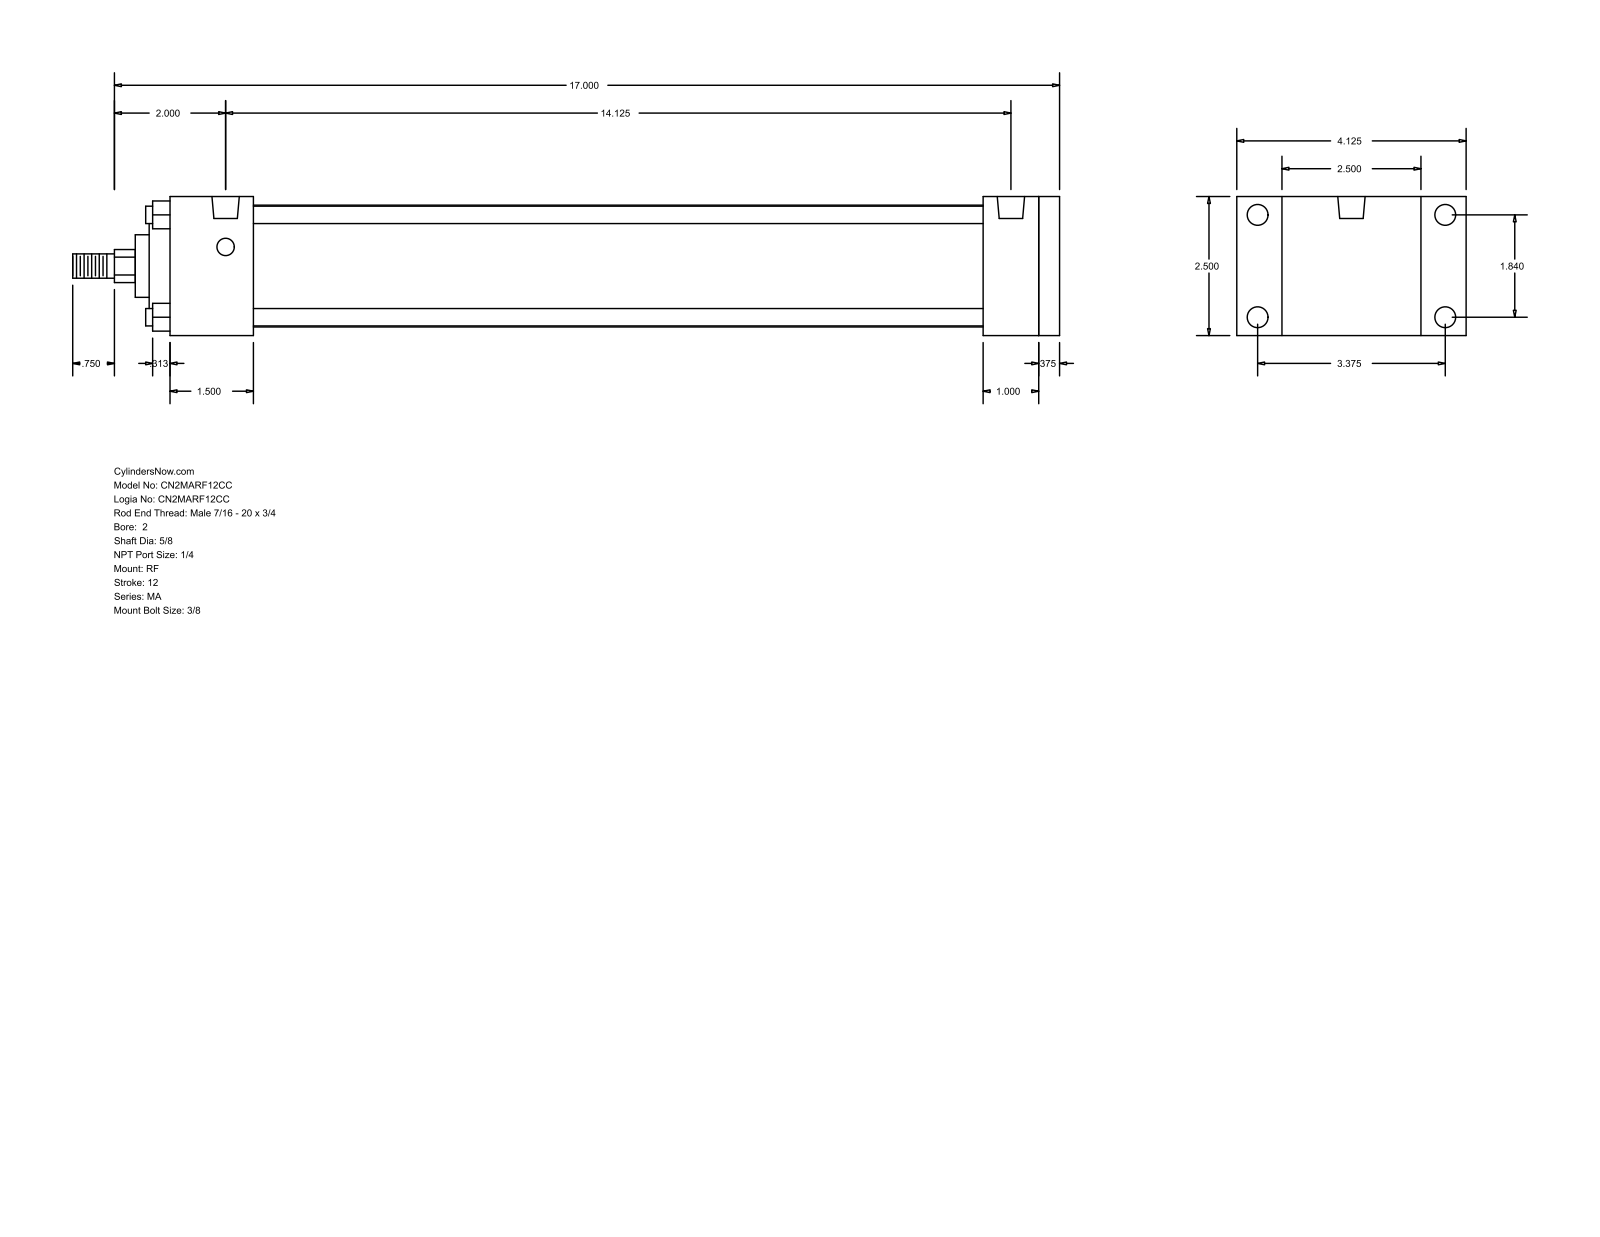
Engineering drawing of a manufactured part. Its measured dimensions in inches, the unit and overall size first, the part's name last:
Units: inches
Overall size (bounding box): 17.75 × 4.125 × 2.5
Round holes (diameter × count): ⌀0.313 ×4, ⌀0.375 ×4, ⌀0.492 ×2
Round bosses / shafts (diameter × count): ⌀0.313 ×4, ⌀2.19 ×1, ⌀2 ×1, ⌀1.125 ×1, ⌀0.625 ×1, ⌀0.437 ×1
Partial cylindrical surfaces — rounded edges, fillets, slot ends (radius × count): R0.297 ×1
Main face-to-face distances: 2.5, 0.375, 1.5, 15.625, 16, 16.375, 14.125, 14.5, 14.625, 13.125
Hole centre spacings: 1.84, 3.375, 3.844, 14.125
Bodies: 0 solids, 94 faces (65 planar, 29 cylindrical, 0 other)
Part name (STEP PRODUCT): MA_RF__0200_0.625
STEP written by: GSSL Pune (CONFIG_CONTROL_DESIGN)
